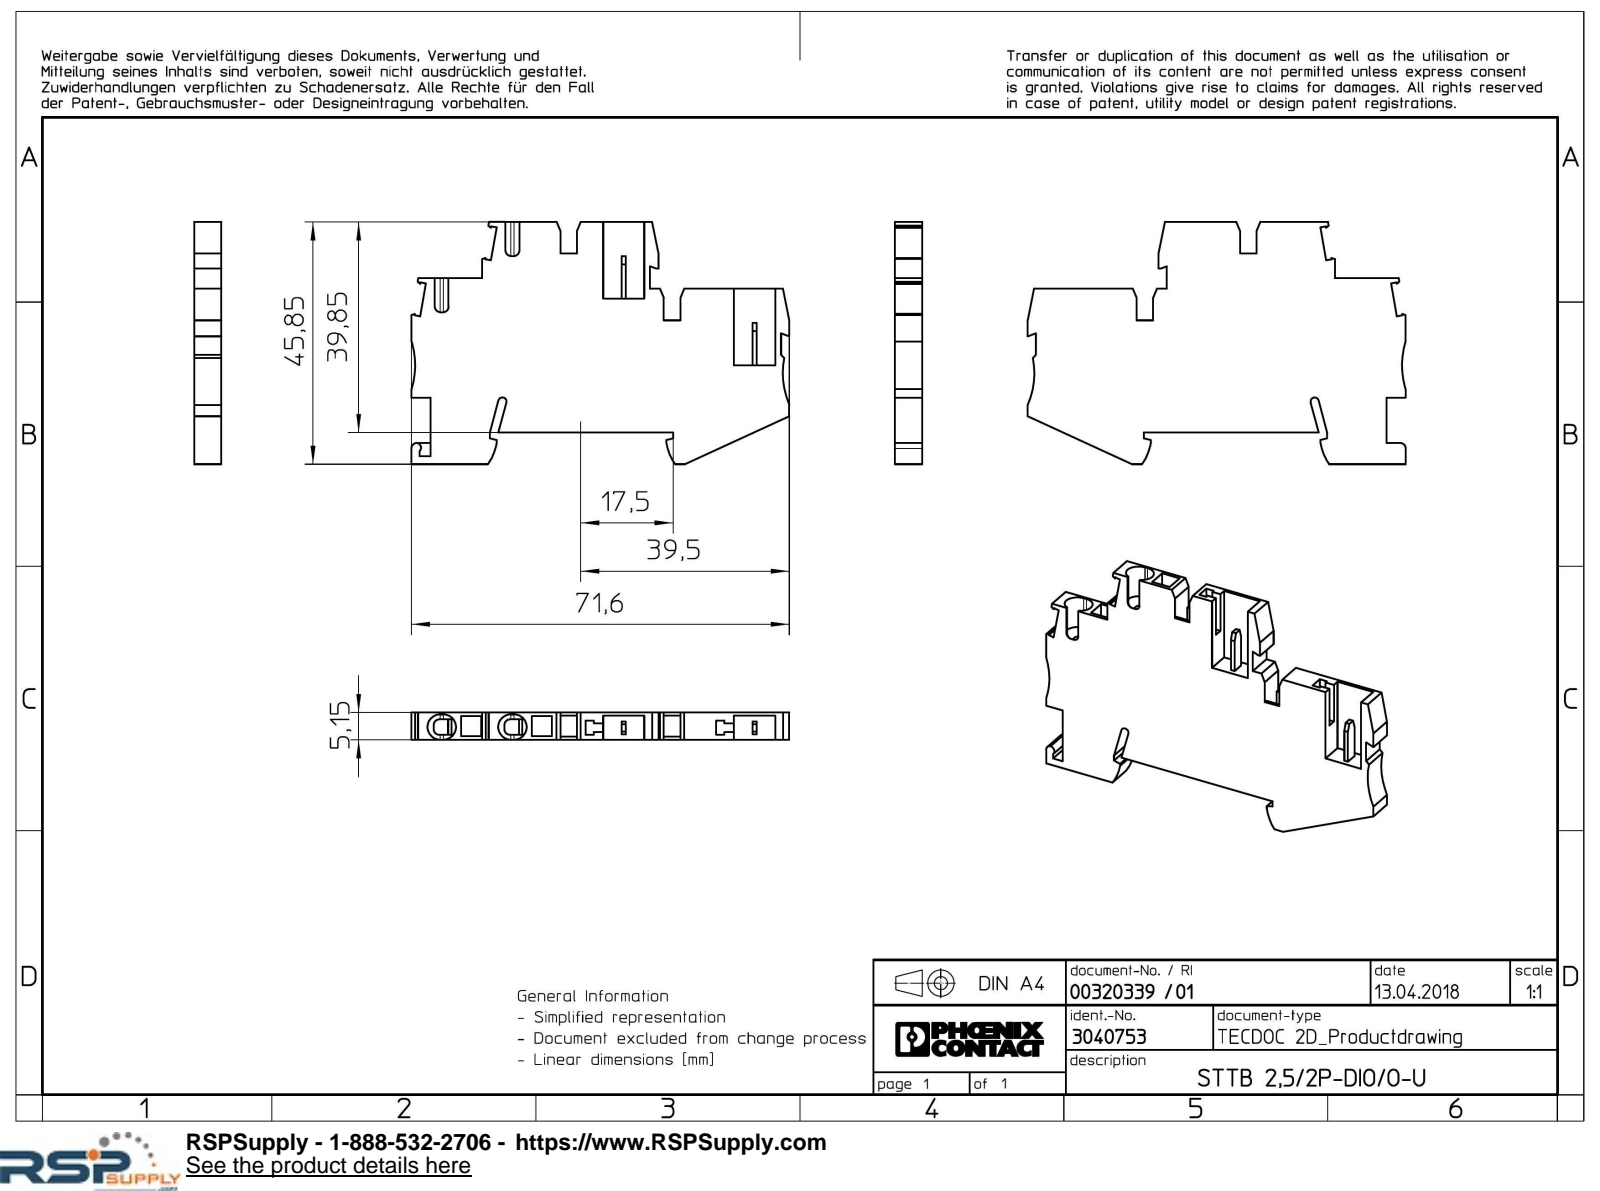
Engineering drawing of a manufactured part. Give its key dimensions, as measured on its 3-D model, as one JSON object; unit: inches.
{"part_name": "STTB-25-2P-DIO-O-U-select", "step_written_by": "Creo Elements/Direct Modeling 18.1I 14-Aug-2016 (C) Parametric Technology GmbH (AUTOMOTIVE_DESIGN)", "units": "inches", "bodies": {"solids": 1, "faces": 174, "planar": 148, "cylindrical": 20, "other": 6}, "overall_size": [2.818, 1.805, 0.203], "volume_in3": 0.626, "surface_area_in2": 11.93, "partial_cylinders_radius": [[0.039, 9], [0.094, 4], [0.374, 2], [0.591, 2], [0.028, 1], [0.031, 1], [0.035, 1]], "face_to_face_distances": [0.203, 0.024, 0.179, 0.124, 0.976, 0.772, 0.146, 0.498, 0.142, 0.307]}
